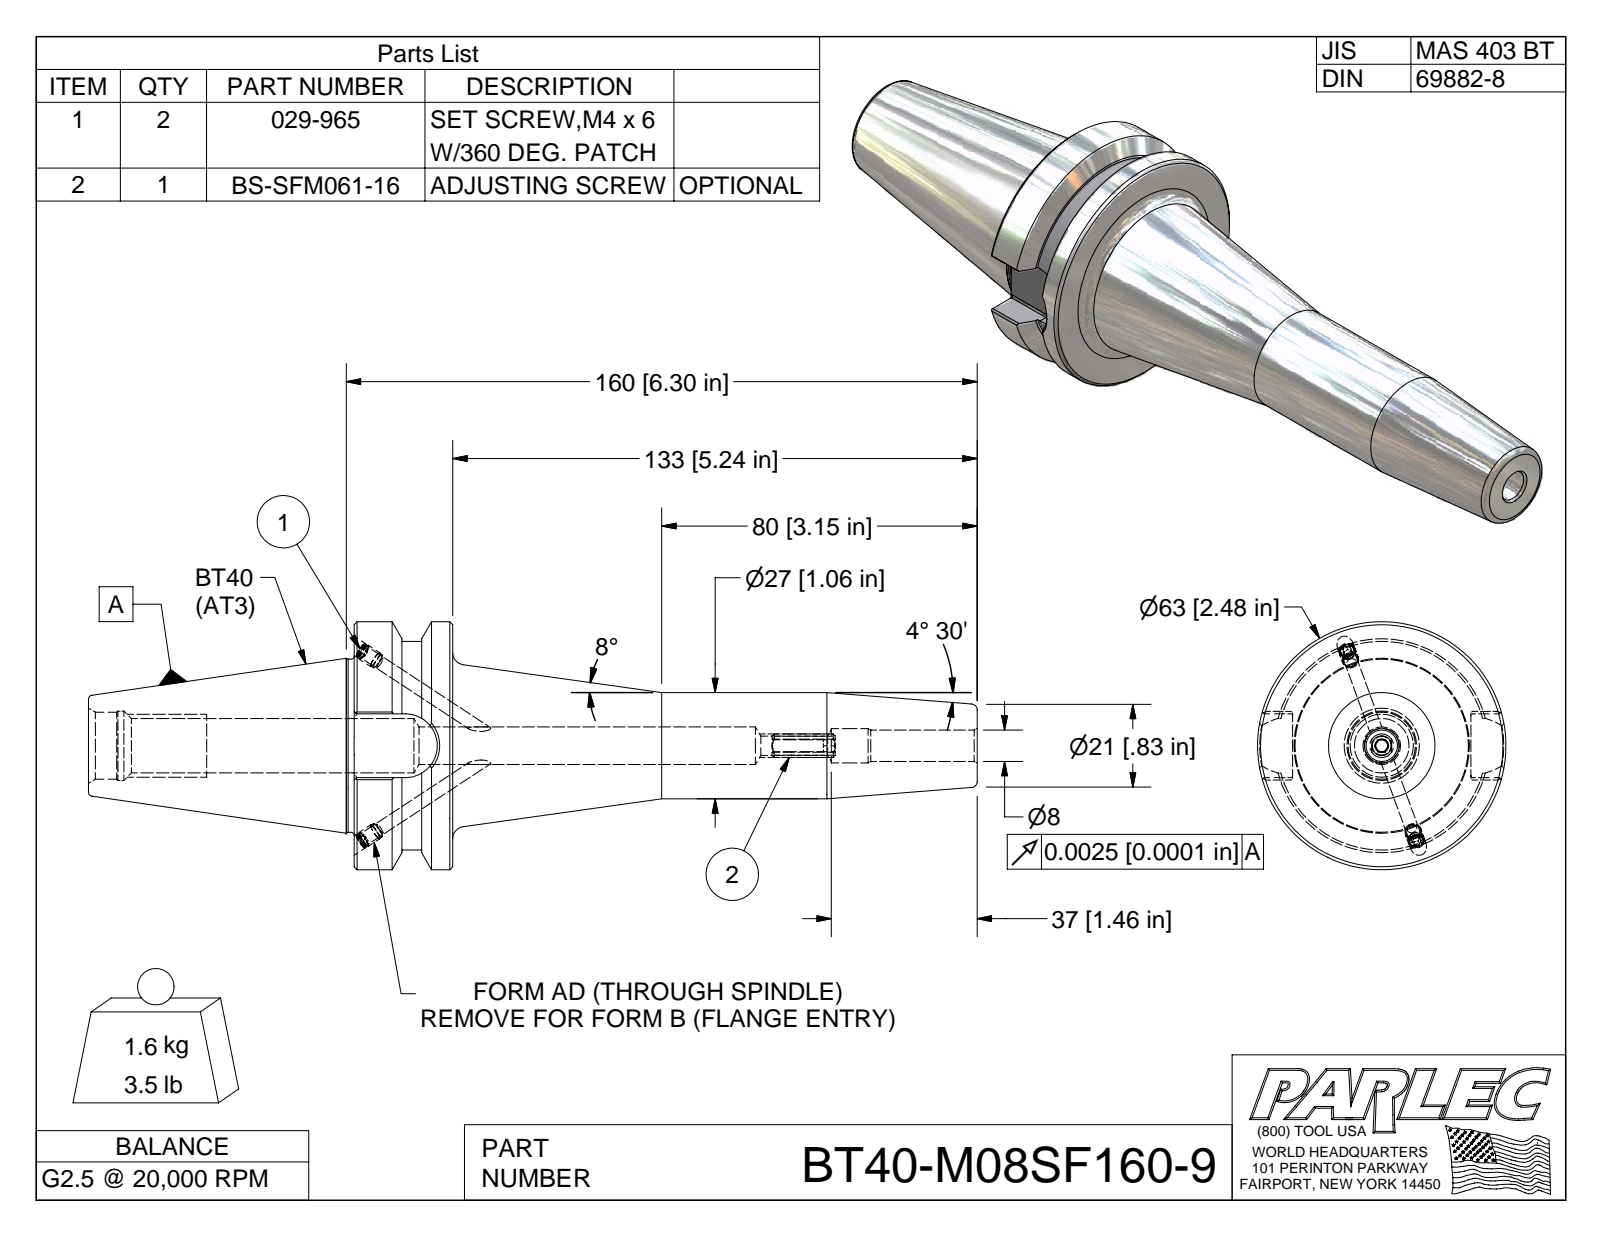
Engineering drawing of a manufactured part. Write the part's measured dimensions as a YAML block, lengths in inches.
part_name: "BT40-M08SF160-9; BT40BC-M08SF160-9-1; 029-965; BS-SFM061-16"
step_written_by: "Autodesk Inventor 2009 (AUTOMOTIVE_DESIGN)"
units: inches
bodies: {solids: 4, faces: 139, planar: 57, cylindrical: 33, other: 49}
overall_size: [8.874, 2.48, 2.48]
volume: 12.43
surface_area: 59.55
round_holes:
  - {diameter: 0.13, count: 2}
  - {diameter: 0.161, count: 2}
  - {diameter: 0.314, count: 1}
  - {diameter: 0.344, count: 1}
  - {diameter: 0.694, count: 1}
round_bosses_or_shafts:
  - {diameter: 0.165, count: 2}
  - {diameter: 0.157, count: 2}
  - {diameter: 2.48, count: 1}
  - {diameter: 2.087, count: 1}
  - {diameter: 1.75, count: 1}
  - {diameter: 1.73, count: 1}
  - {diameter: 1.063, count: 1}
partial_cylinders:
  - {radius: 0.02, count: 8}
  - {radius: 0.118, count: 1}
  - {radius: 0.319, count: 1}
face_to_face_distances: [0.984, 1.78, 6.221, 5.237, 2.653, 3.637, 8.874, 0.637, 0.197, 0.792]
